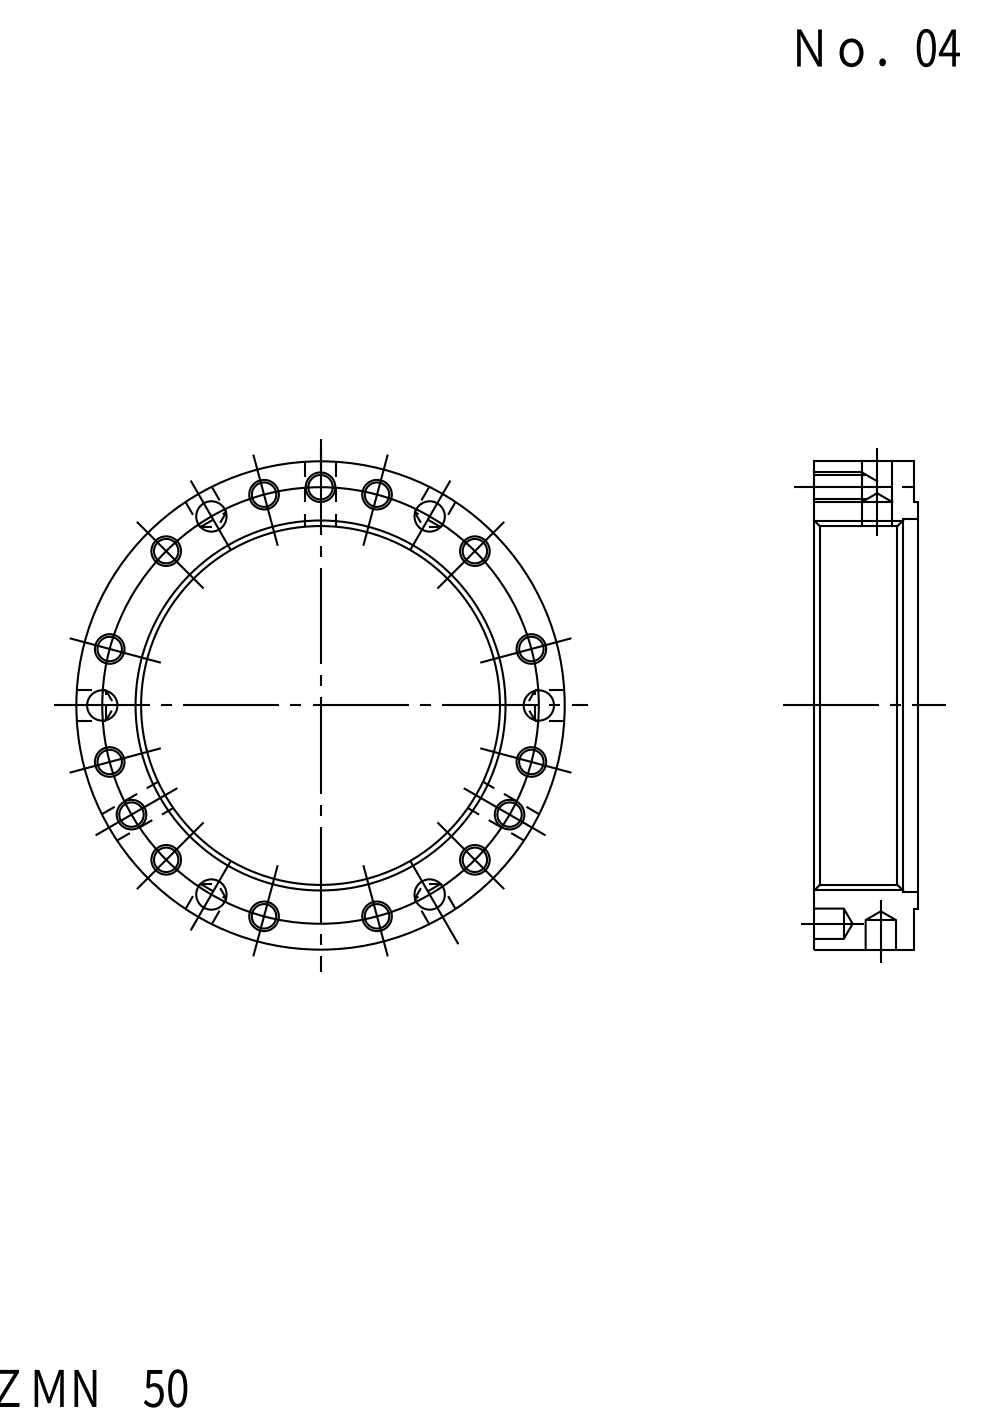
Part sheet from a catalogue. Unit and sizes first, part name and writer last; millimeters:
Units: millimetres
Overall size (bounding box): 66 × 66 × 14
Round holes (diameter × count): ⌀3.24 ×15, ⌀4.1 ×12, ⌀50 ×1, ⌀50.5 ×1
Round bosses / shafts (diameter × count): ⌀66 ×1, ⌀55 ×1
Main face-to-face distances: 13.5, 0.5, 14, 1.5, 1, 12.5
Hole centre spacings: 29.5, 54.51, 56.99, 51.1, 22.58, 35.92, 46.81, 58.49
Volume: 17 774 mm³ · Surface area: 10 087 mm²
Bodies: 1 solid, 62 faces (4 planar, 34 cylindrical, 24 other)
Part name (STEP PRODUCT): FKD ZMN50
STEP written by: Autodesk Inventor LT (CONFIG_CONTROL_DESIGN)
